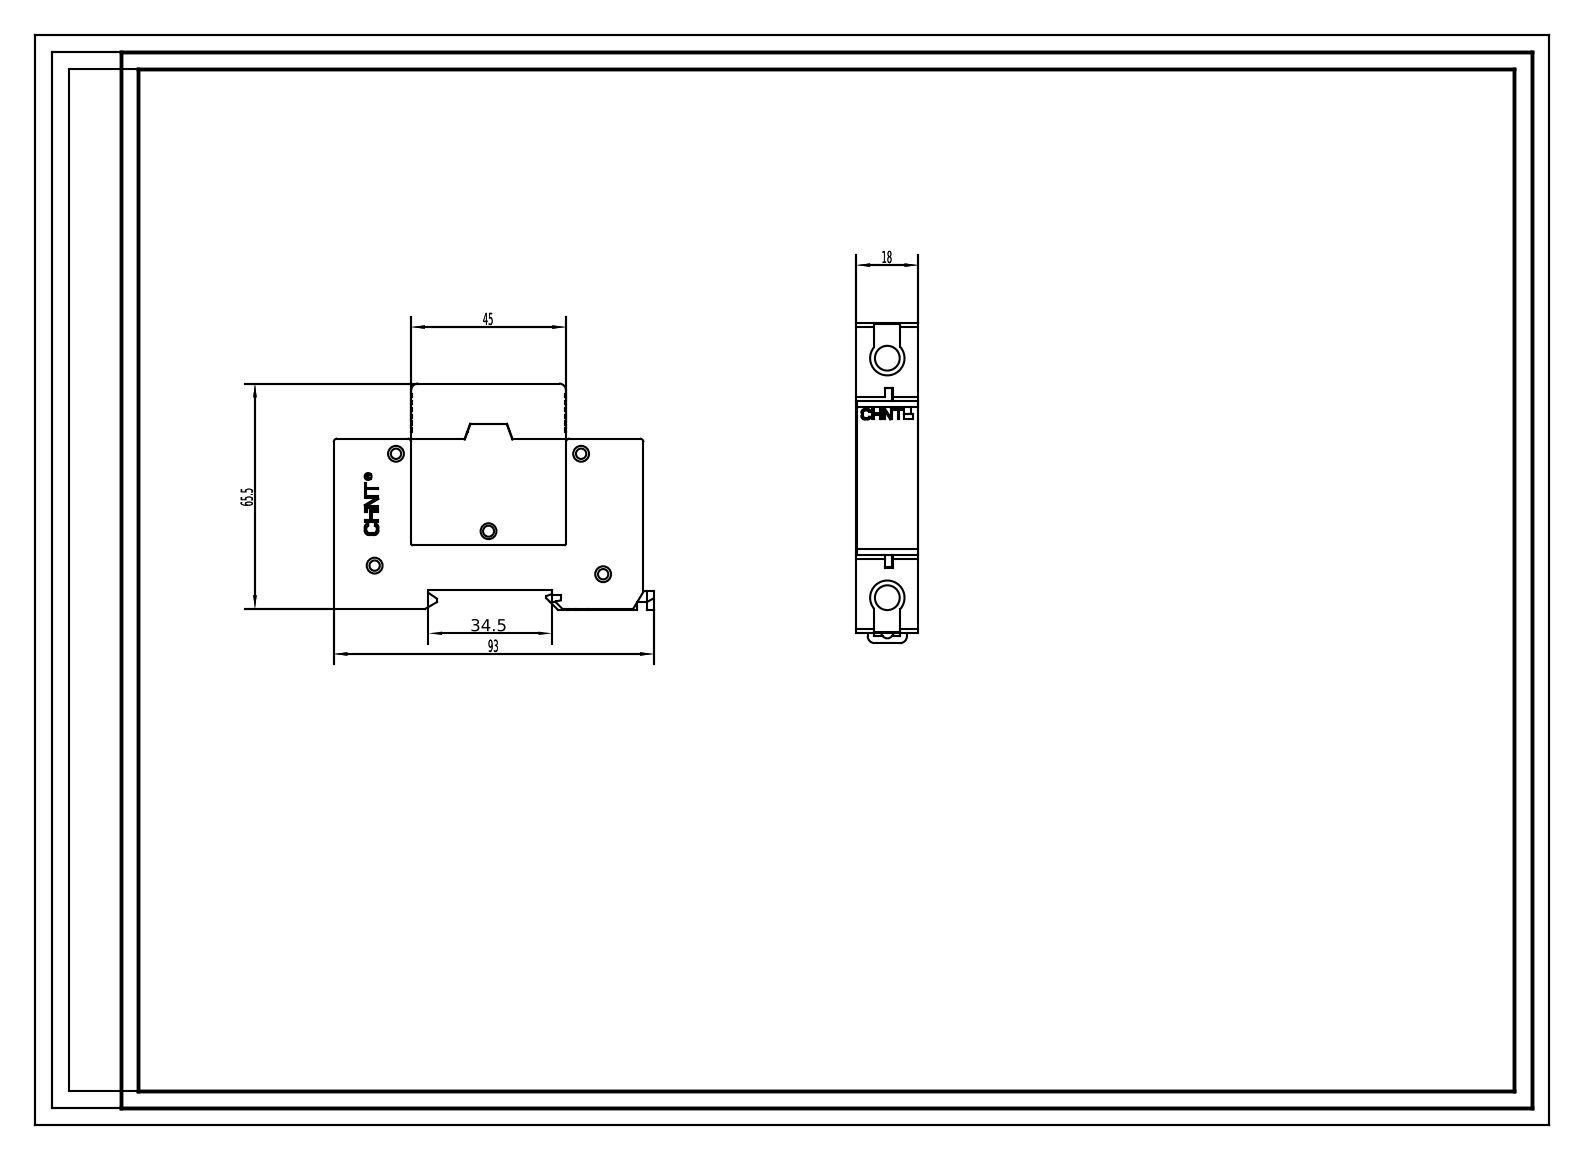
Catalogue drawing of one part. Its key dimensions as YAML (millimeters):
part_name: "8-005-220; 8-005-219; 8-315-395; 5-573-092_18_ASM (+6 more)"
step_written_by: "PRO/ENGINEER BY PARAMETRIC TECHNOLOGY CORPORATION, 2010280 (CONFIG_CONTROL_DESIGN)"
units: millimeters
bodies: {solids: 7, faces: 2416, planar: 2221, cylindrical: 191, other: 4}
overall_size: [93, 65.7, 18]
volume: 50801
surface_area: 44919
round_holes:
  - {diameter: 4.6, count: 5}
  - {diameter: 3, count: 4}
  - {diameter: 2, count: 2}
  - {diameter: 2.5, count: 2}
  - {diameter: 2.6, count: 2}
  - {diameter: 4.8, count: 2}
  - {diameter: 7.2, count: 2}
  - {diameter: 3.2, count: 1}
partial_cylinders:
  - {radius: 1, count: 26}
  - {radius: 0.5, count: 23}
  - {radius: 2, count: 18}
  - {radius: 1.5, count: 6}
  - {radius: 0.2, count: 5}
  - {radius: 0.33, count: 3}
  - {radius: 0.37, count: 3}
  - {radius: 0.8, count: 3}
face_to_face_distances: [1.5, 16.5, 16.3, 8, 8.2, 8.3, 16.1, 9.7, 1.6, 1.7]
hole_center_spacings: [17.17, 35.07, 53.05, 8, 10.08, 10.45, 16, 24.01]
